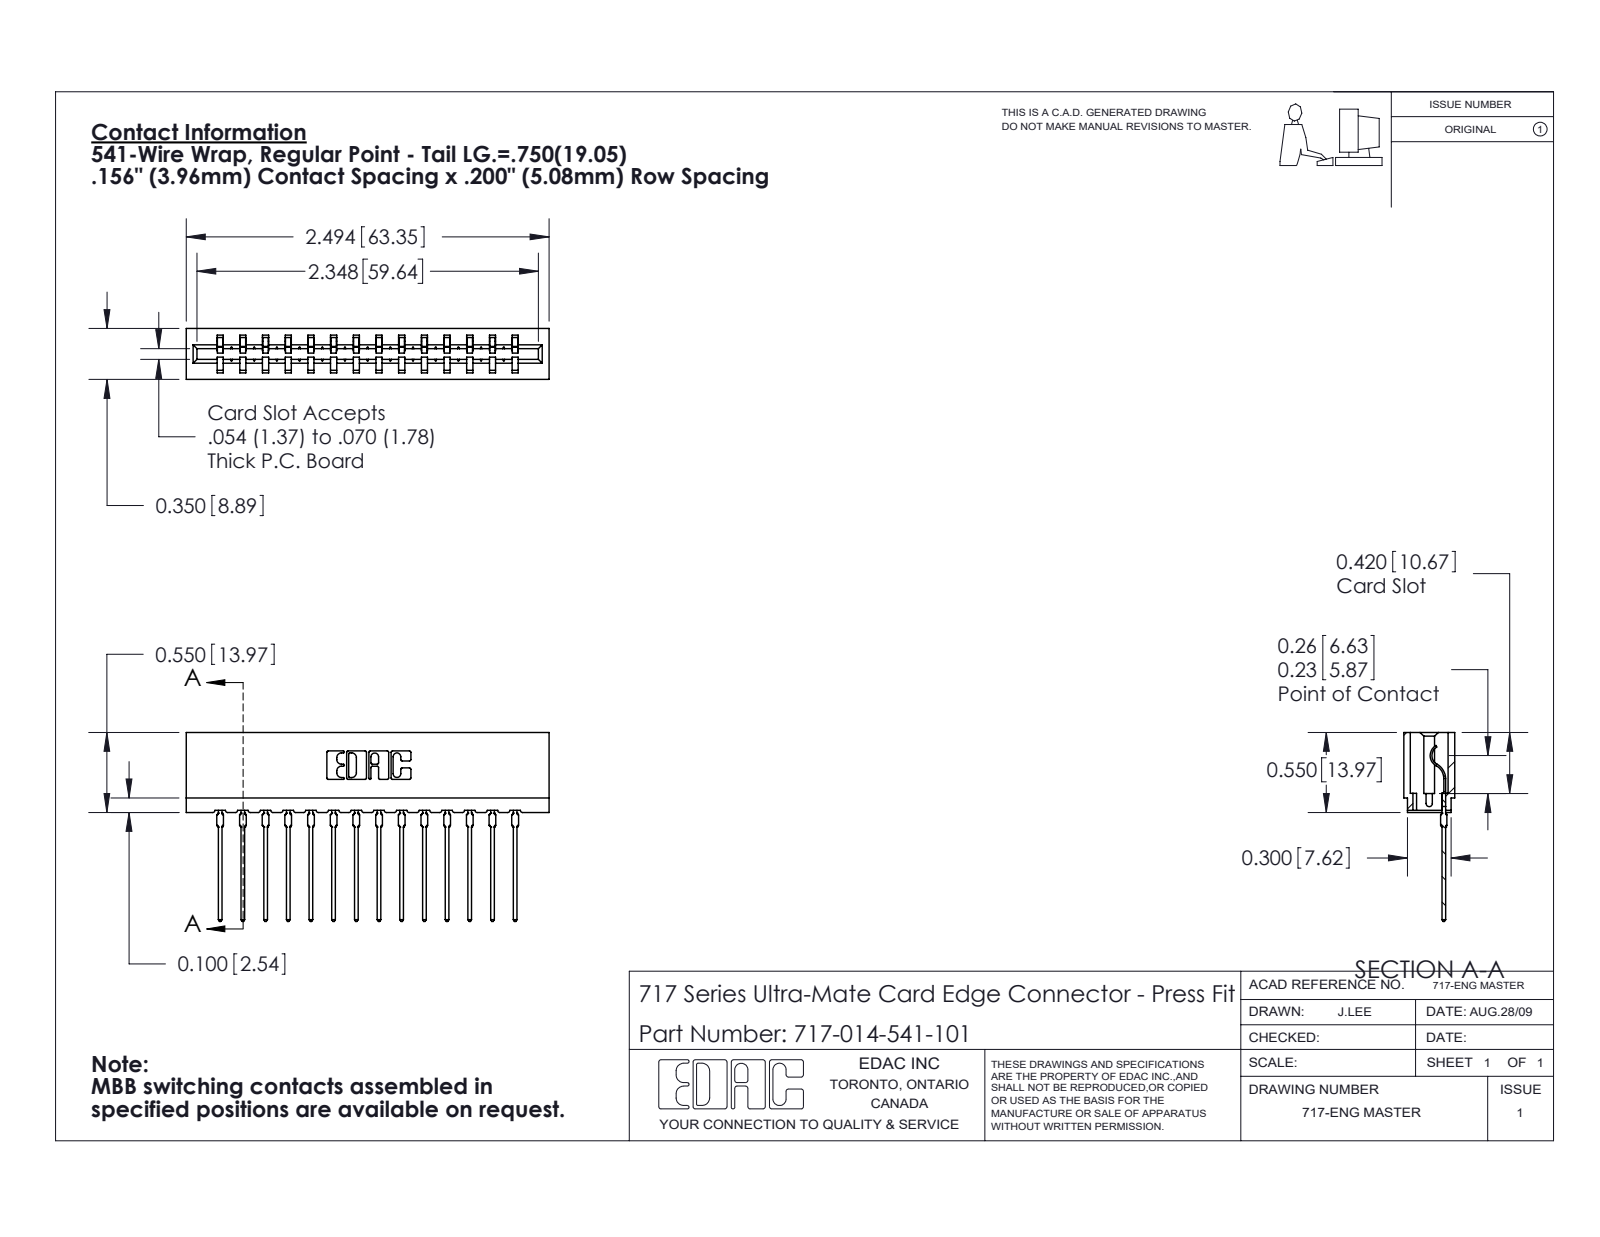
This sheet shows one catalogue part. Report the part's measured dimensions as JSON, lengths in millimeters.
{"part_name": "717 Part_Insulator Option - 06; 745-292-001_541; 717-014-541-101", "step_written_by": "SolidWorks 2020 (CONFIG_CONTROL_DESIGN)", "units": "millimeters", "bodies": {"solids": 15, "faces": 1676, "planar": 1006, "cylindrical": 306, "other": 364}, "overall_size": [63.3, 33, 8.9], "volume_mm3": 5540, "surface_area_mm2": 7768, "partial_cylinders_radius": [[0.4, 28], [0.5, 28], [0.3, 22], [0.2, 6], [0.8, 6], [0.1, 4], [0.3, 4], [0.7, 3]], "face_to_face_distances": [5.4, 3.5, 4, 8.9, 15.8, 5, 7.9, 11.9, 1.9, 1.6]}
